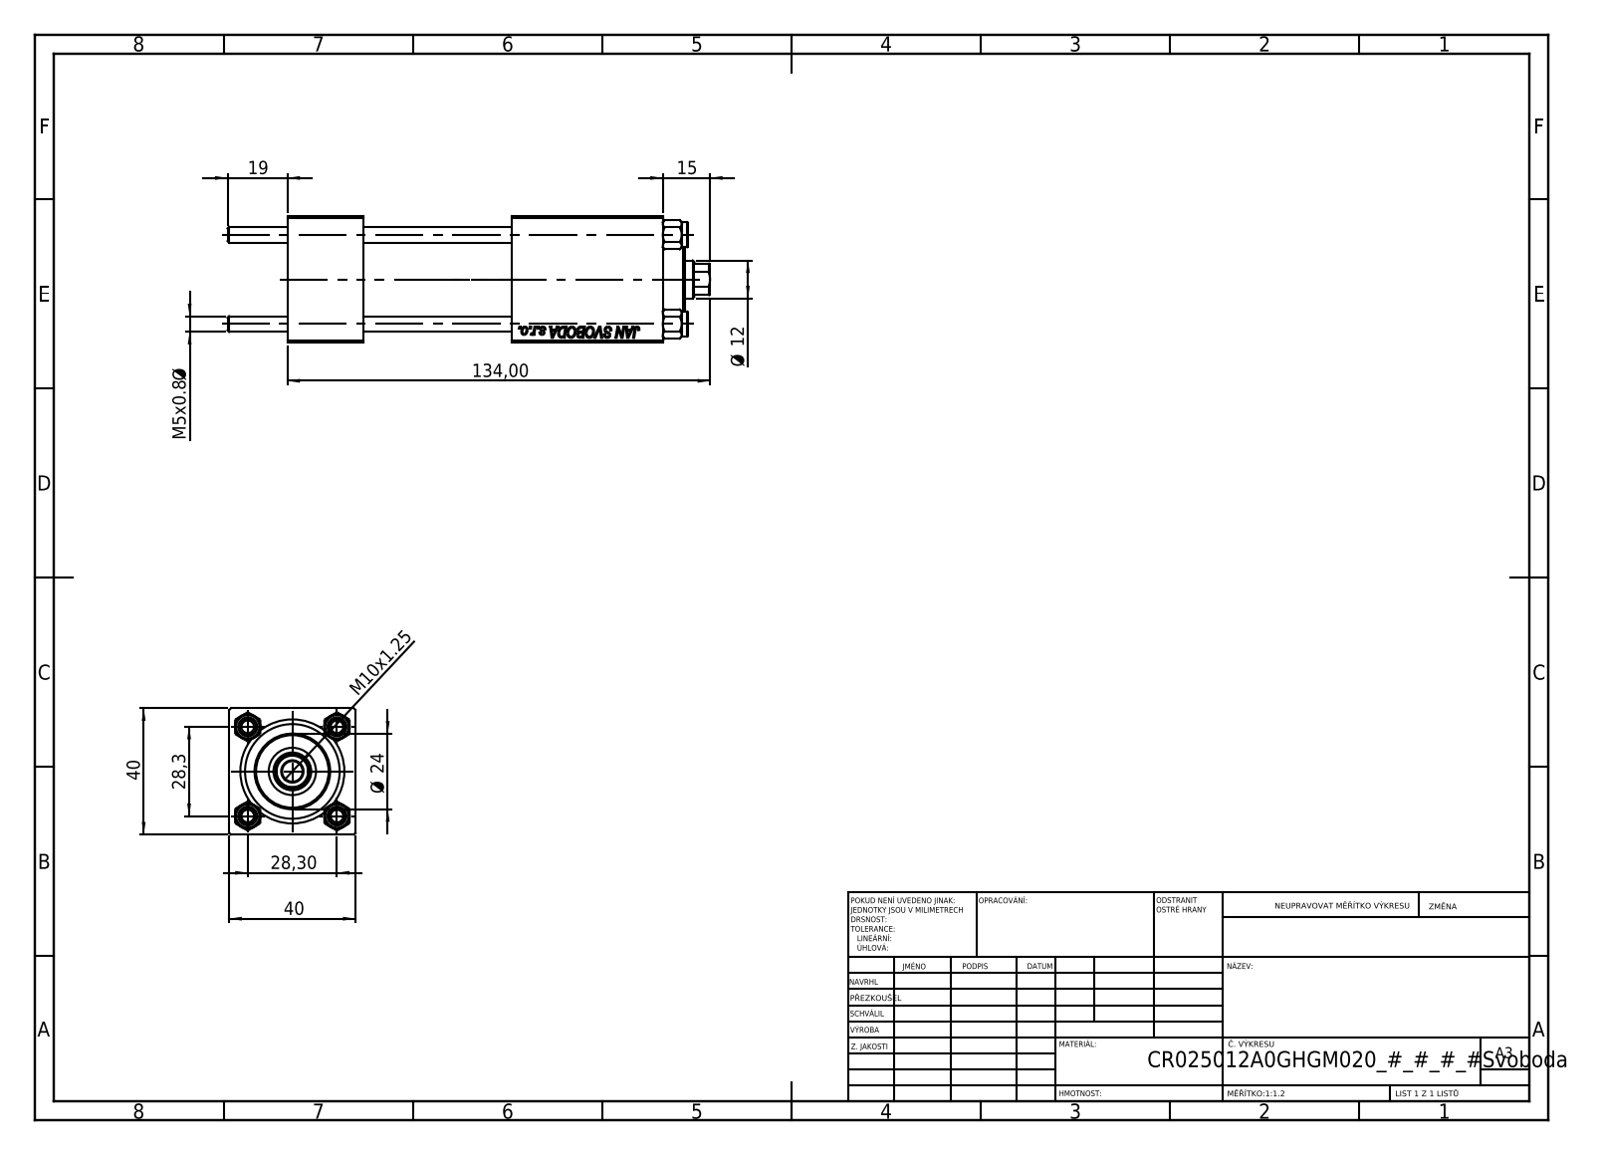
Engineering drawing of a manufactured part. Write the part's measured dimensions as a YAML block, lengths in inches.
part_name: "V215CR_BODY_A; CR025_012_A_0_G_A_G_M_020_+#_##_TYCINKA; NUT_M5; V215_VC_A (+1 more)"
step_written_by: "SolidWorks 2019 (CONFIG_CONTROL_DESIGN)"
units: inches
bodies: {solids: 11, faces: 1131, planar: 517, cylindrical: 78, other: 536}
overall_size: [6.024, 1.575, 1.575]
volume: 8.838
surface_area: 91.25
round_holes:
  - {diameter: 0.197, count: 4}
  - {diameter: 0.787, count: 3}
  - {diameter: 0.276, count: 2}
  - {diameter: 0.518, count: 2}
  - {diameter: 0.256, count: 1}
  - {diameter: 0.472, count: 1}
  - {diameter: 0.591, count: 1}
  - {diameter: 0.984, count: 1}
  - {diameter: 1.181, count: 1}
round_bosses_or_shafts:
  - {diameter: 0.315, count: 4}
  - {diameter: 1.22, count: 1}
  - {diameter: 0.945, count: 1}
partial_cylinders:
  - {radius: 0.217, count: 1}
face_to_face_distances: [1.575, 0.945, 4.685, 3.74, 3.555, 2.61, 1.13, 2.795, 1.85, 0.76]
hole_center_spacings: [0.788, 1.114, 1.576, 2.835]
